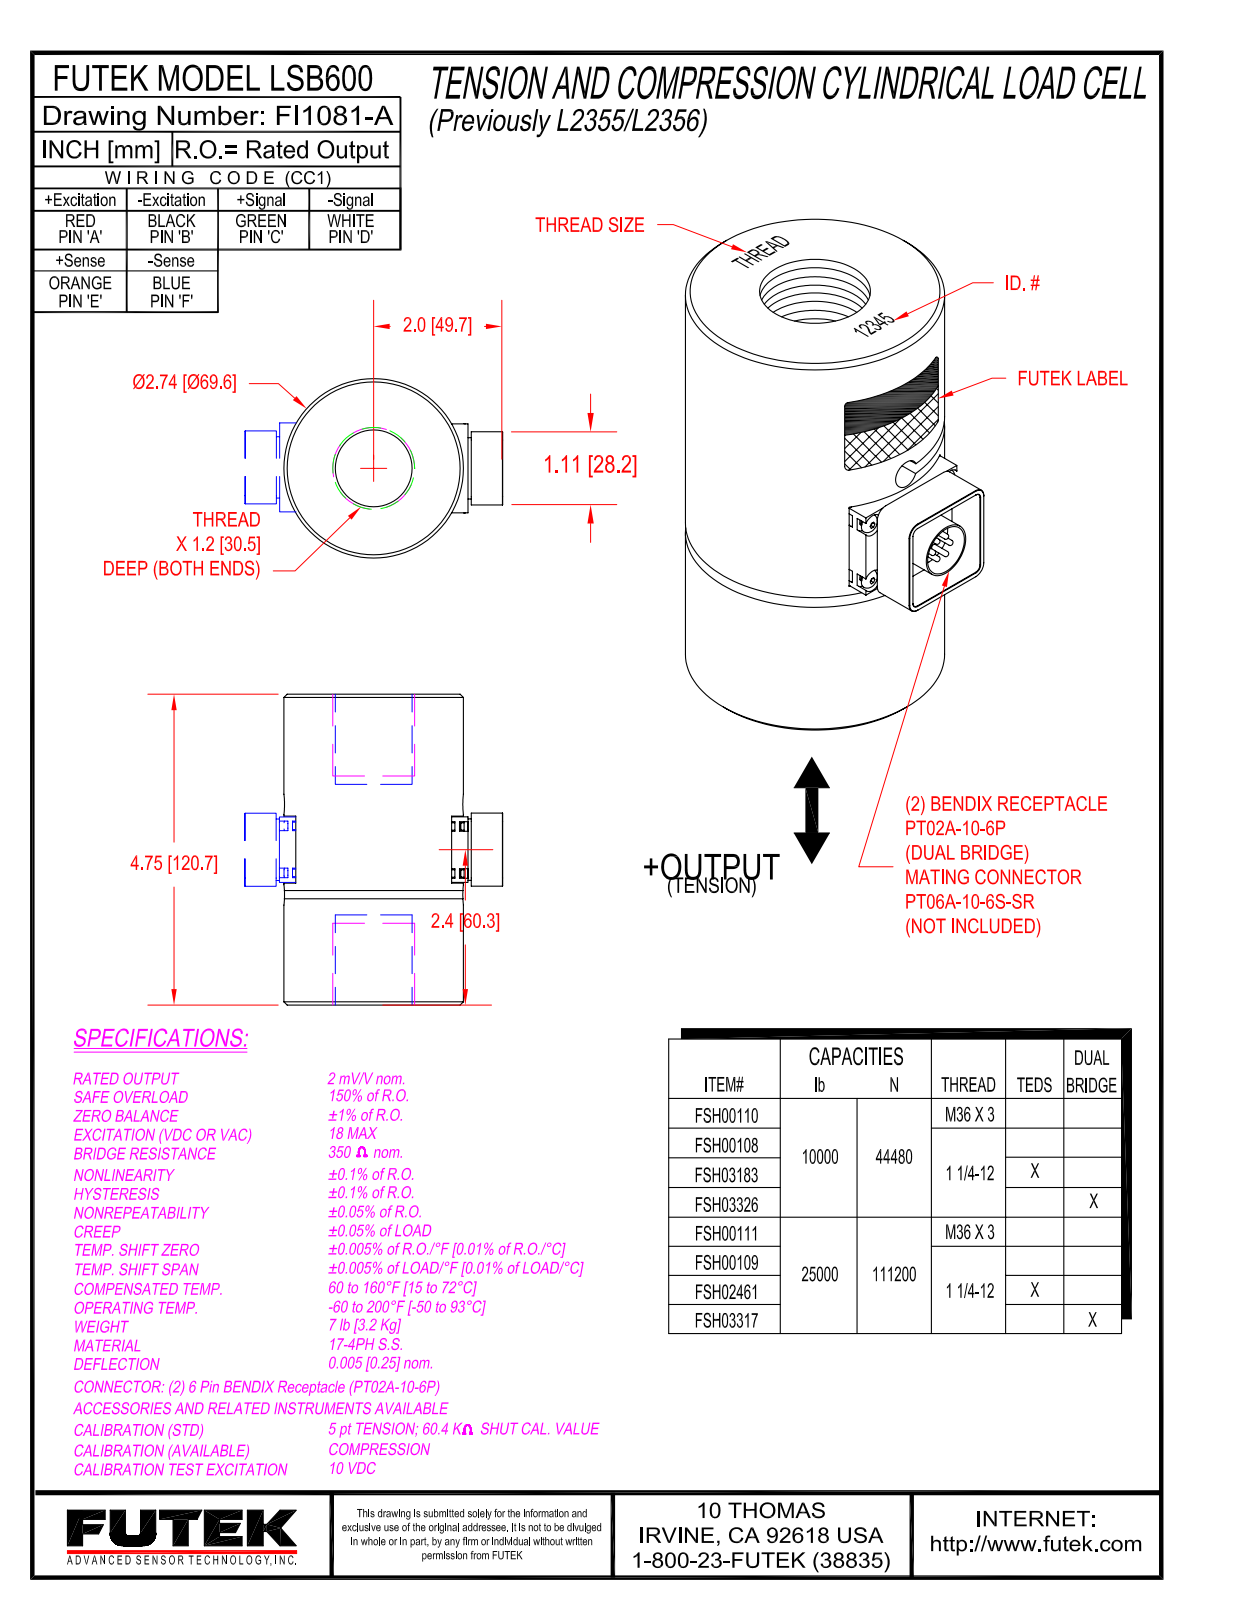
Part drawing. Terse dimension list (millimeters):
name: LSB600 1 1-4 Thread Bendix Single Bridge; $F1334-C
written by: Autodesk Inventor 2008 (AUTOMOTIVE_DESIGN)
unit: mm
bodies: 1 solid, 194 faces (107 planar, 57 cylindrical, 30 other)
size: 120.7 × 84.8 × 69.6
volume: 414 100 mm³; area: 49 200 mm²
holes: 4× ⌀2.3, 4× ⌀3.2, 4× ⌀3.3, 2× ⌀4.8, 1× ⌀1.3, 1× ⌀14, 1× ⌀15.9, 1× ⌀17.5, 1× ⌀25.7, 1× ⌀29.8
bosses: 6× ⌀1.5, 4× ⌀4.6, 4× ⌀2.8, 1× ⌀69.6, 1× ⌀25.5, 1× ⌀15, 1× ⌀14.6
rounds: 4× R1.3, 4× R1.6, 4× R3.2
face distances: 120.7, 33, 87.6, 1.5, 26.9, 54.6, 25.4, 46.2, 74.5, 13.1
hole spacings: 5.6, 9.1, 12.9, 14.7, 17.3, 18.3, 19.1, 23.9
